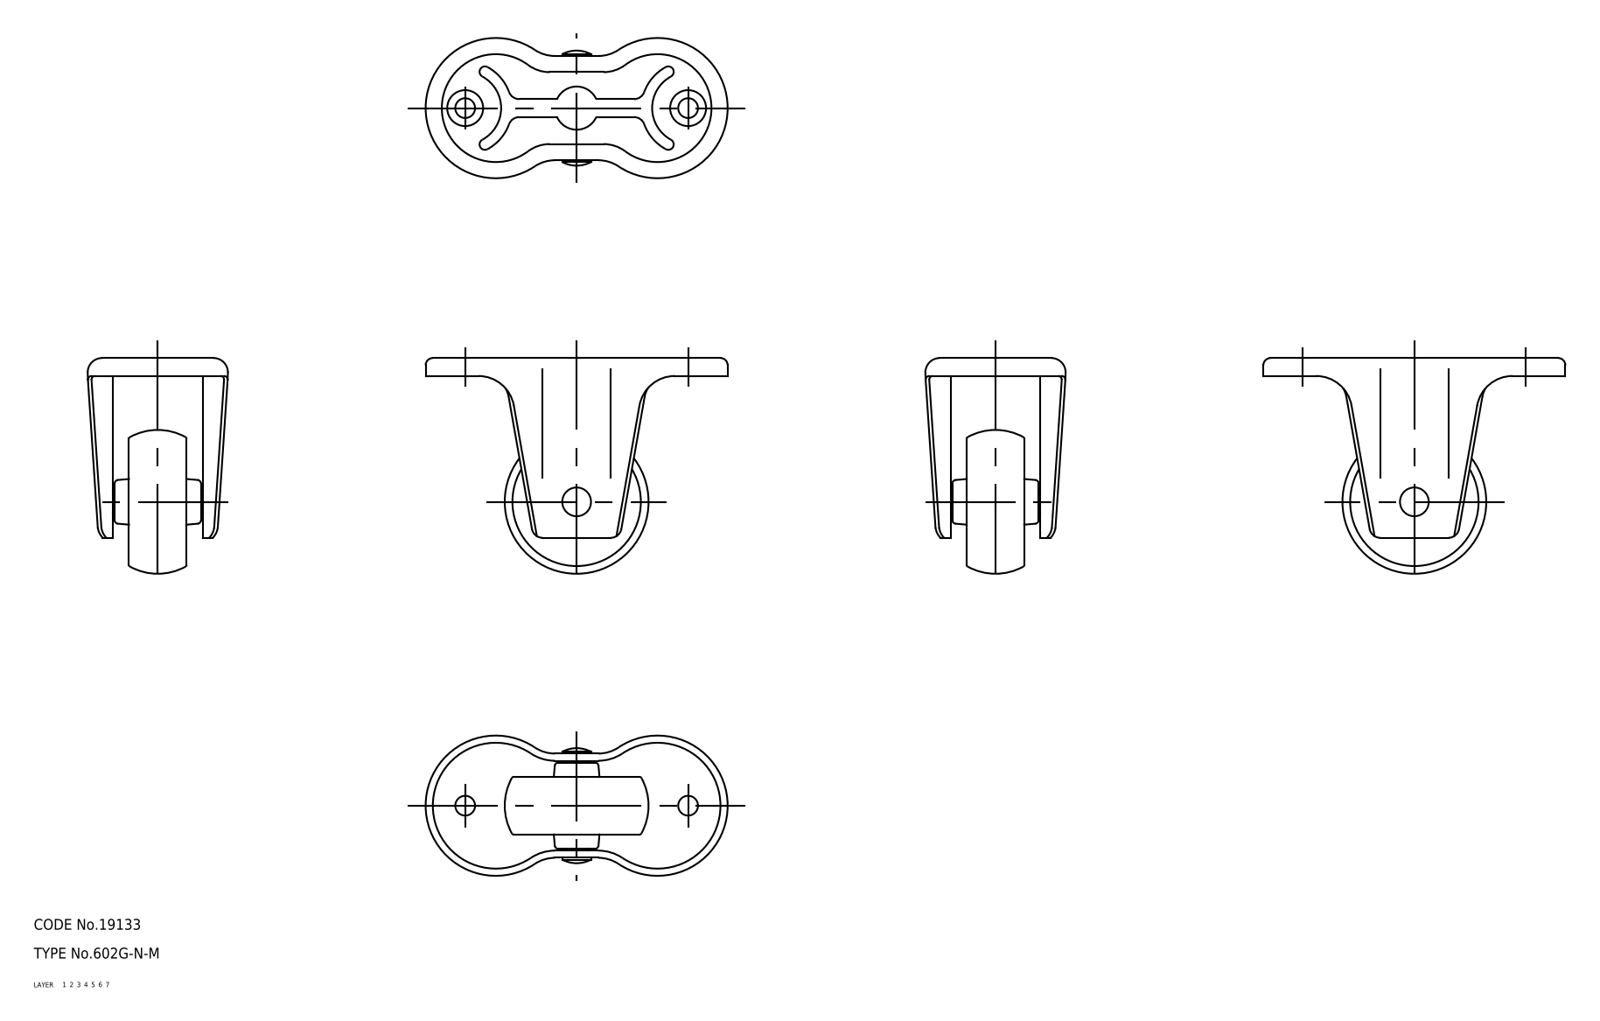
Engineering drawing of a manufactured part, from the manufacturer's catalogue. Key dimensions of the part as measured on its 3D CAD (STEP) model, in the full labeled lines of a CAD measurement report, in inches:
Part name (STEP PRODUCT): wheel; axle; No_602G_N_M_13741_36
STEP written by: CADfix (AUTOMOTIVE_DESIGN)
Units: inches
Bodies: 3 solids, 170 faces (0 planar, 0 cylindrical, 170 other)
Overall size (bounding box): 3.307 × 2.362 × 1.535
Volume: 1.897 in³ · Surface area: 30.32 in²
